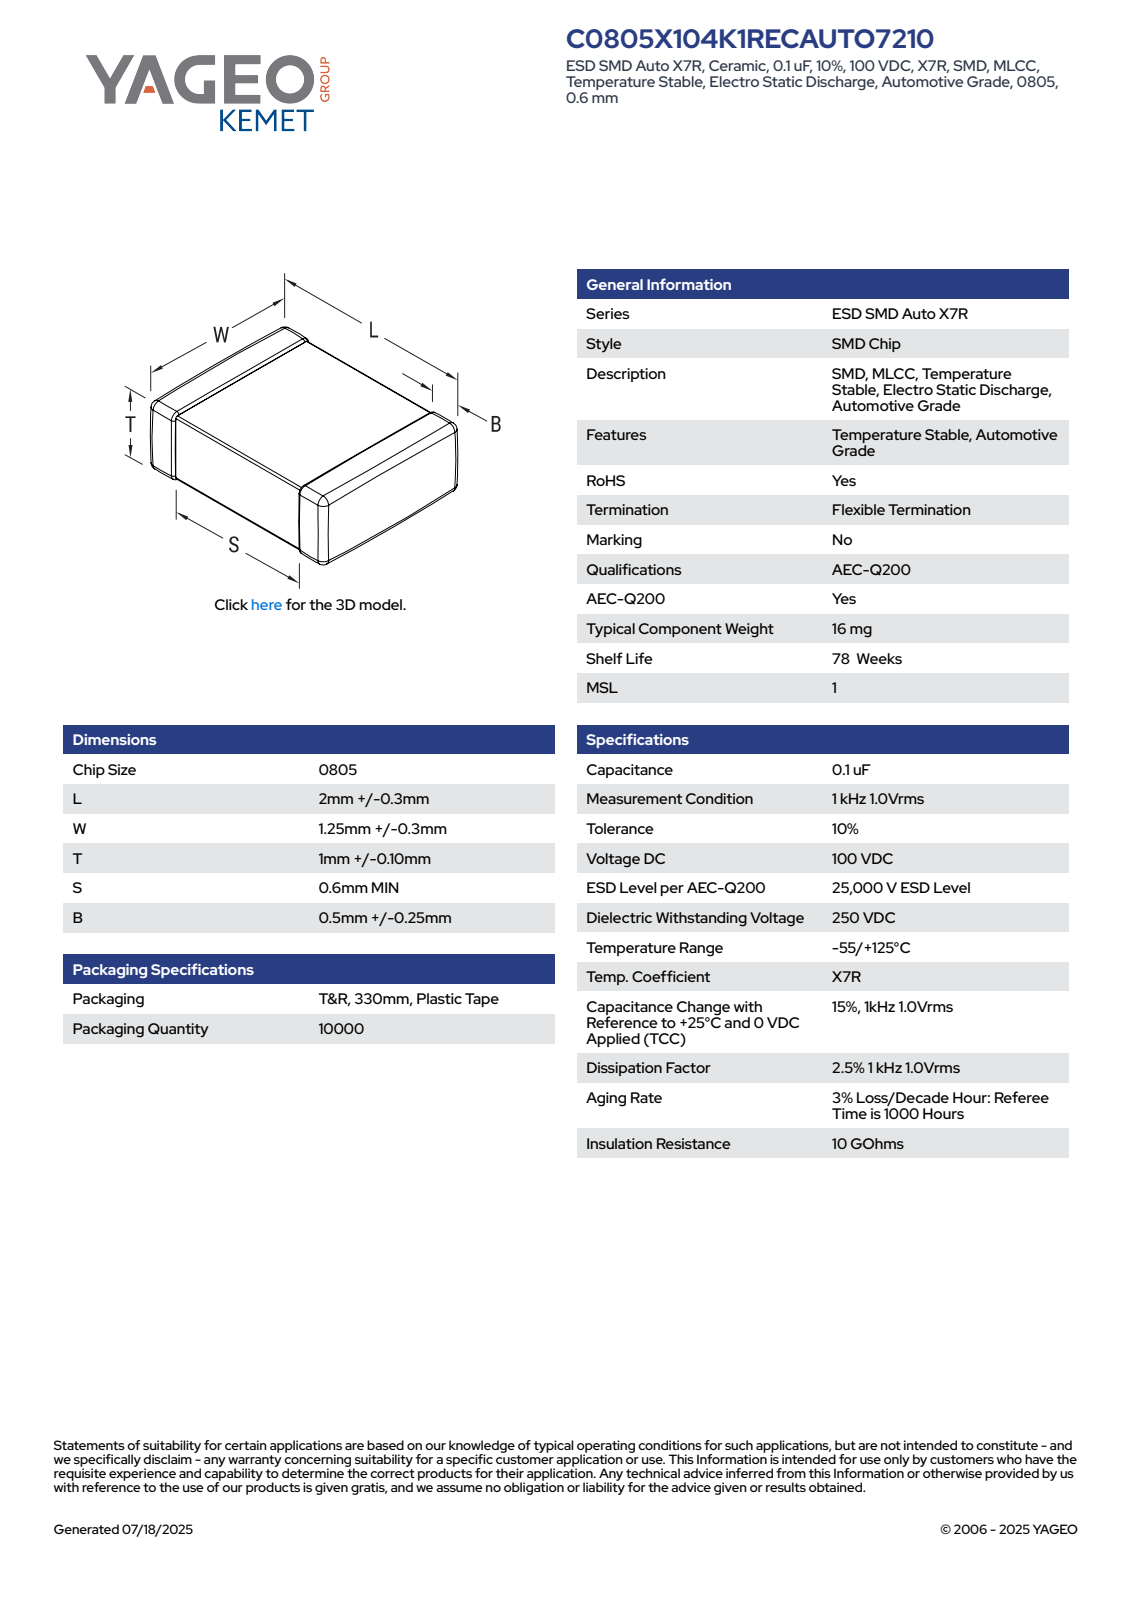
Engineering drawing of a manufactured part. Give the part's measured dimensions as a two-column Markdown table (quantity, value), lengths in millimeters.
| quantity | value |
| --- | --- |
| part name | CCS_CCSTD_0805_L2.3W1.55T1.1B0.5 |
| STEP written by | SolidWorks 2021 (AUTOMOTIVE_DESIGN) |
| units | millimeters |
| bodies | 4 solids, 125 faces (71 planar, 38 cylindrical, 16 other) |
| overall size | 2.3 × 1.55 × 1.1 |
| volume | 4 mm³ |
| surface area | 16 mm² |
| main face-to-face distances | 1.07, 1.1, 1.52, 2.3, 1.55, 1.04, 1.49, 1.06, 1.24, 1.01 |
